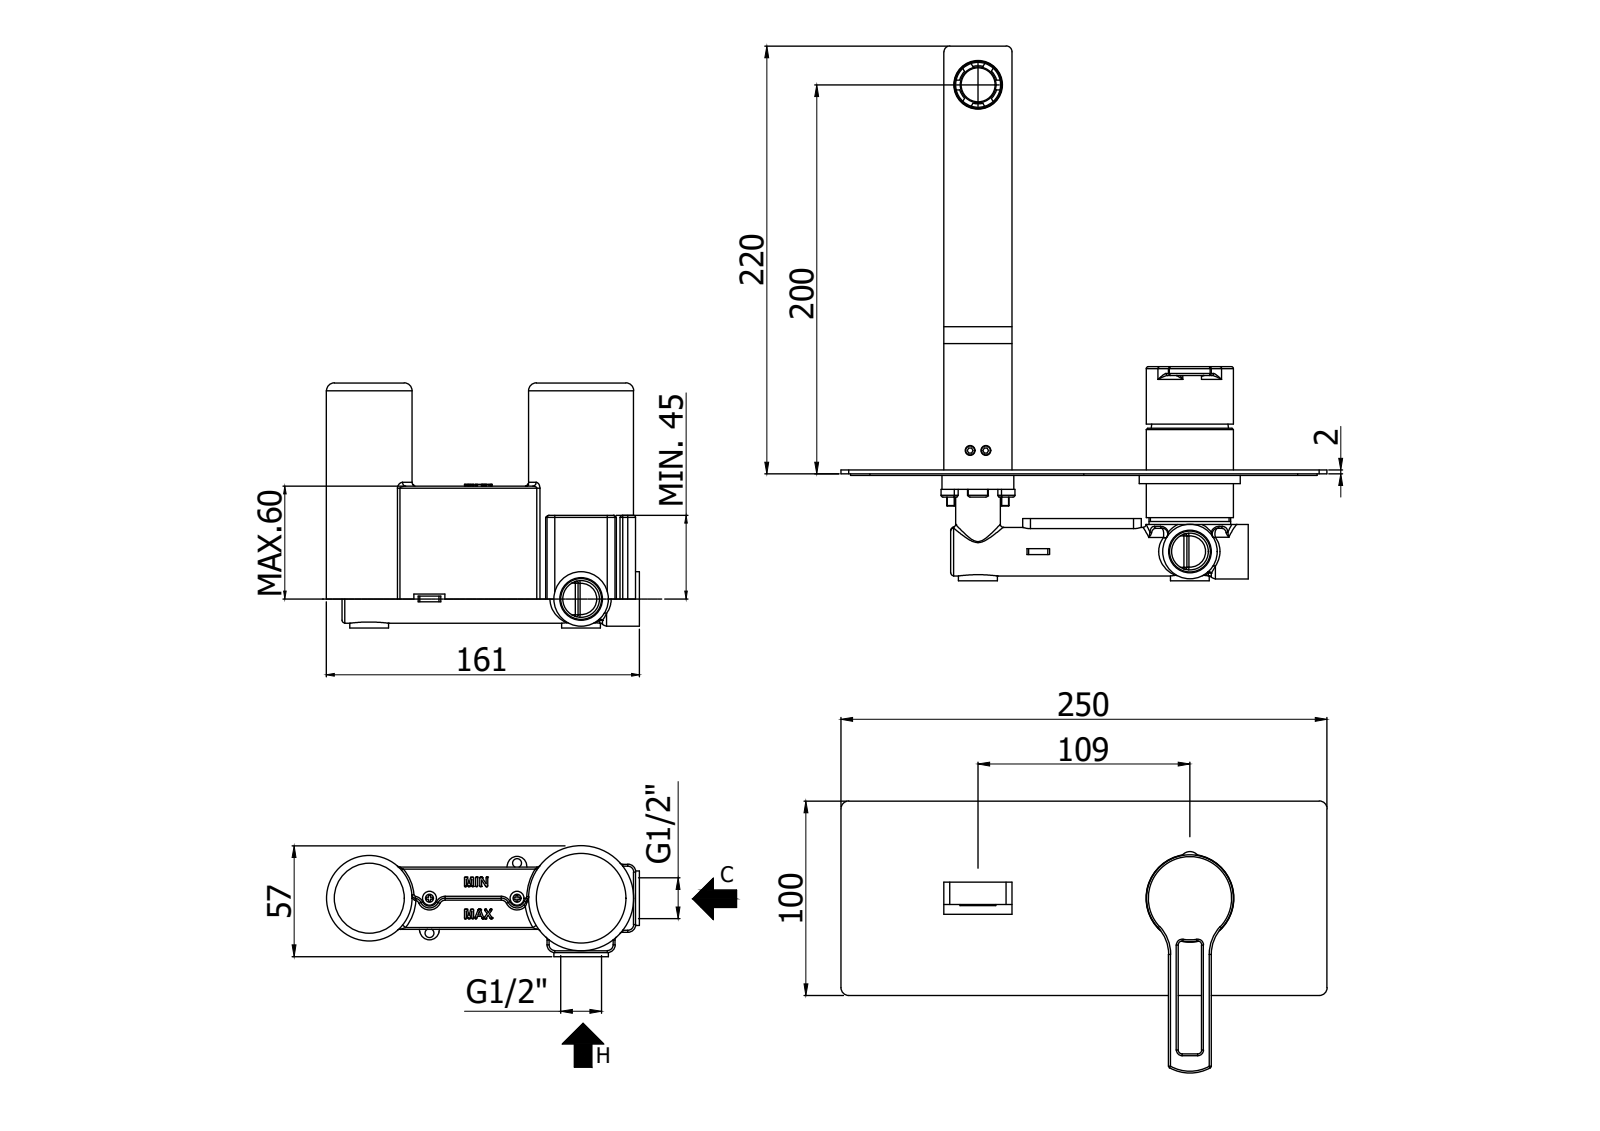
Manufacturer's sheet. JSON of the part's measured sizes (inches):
{"part_name": "RIN105CR", "step_written_by": "CREO PARAMETRIC BY PTC INC, 2020044 (CONFIG_CONTROL_DESIGN)", "units": "inches", "bodies": {"solids": 3, "faces": 1115, "planar": 617, "cylindrical": 268, "other": 230}, "overall_size": [9.843, 8.661, 5.512], "volume_in3": 10.95, "surface_area_in2": 173.5, "round_holes": [[0.157, 2], [0.236, 2], [0.118, 1], [0.13, 1], [0.197, 1], [0.307, 1], [0.433, 1], [0.472, 1], [0.512, 1], [0.591, 1], [0.669, 1], [0.689, 1]], "round_bosses_or_shafts": [[1.764, 1], [1.378, 1], [0.925, 1], [0.921, 1], [0.858, 1], [0.728, 1], [0.465, 1], [0.425, 1]], "partial_cylinders_radius": [[0.02, 14], [0.039, 14], [0.006, 11], [0.012, 4], [0.079, 4], [0.157, 4], [0.083, 2], [0.098, 2]], "face_to_face_distances": [0.079, 0.453, 1.378, 0.197, 0.65, 2.031, 1.953, 0.059, 0.039, 1.644], "hole_center_spacings": [0.433, 4.291, 7.651, 8.014]}
